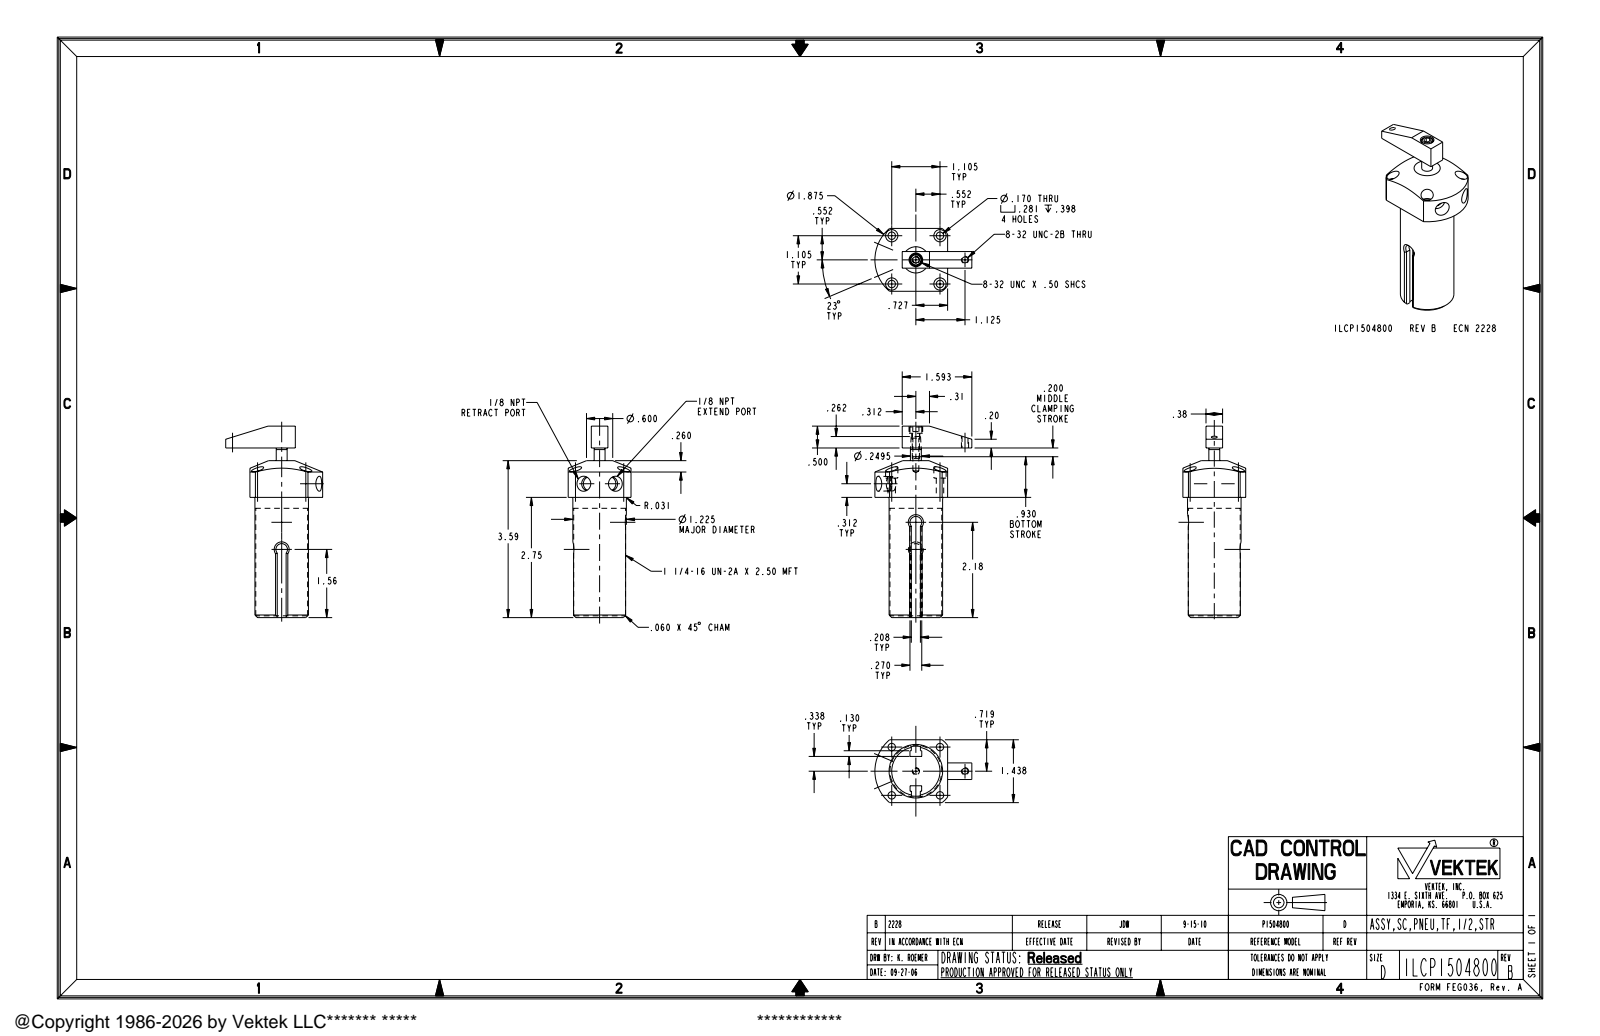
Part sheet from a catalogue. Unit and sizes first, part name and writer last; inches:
Units: inches
Overall size (bounding box): 4.38 × 2.219 × 1.438
Round holes (diameter × count): ⌀0.17 ×4, ⌀0.281 ×4, ⌀0.136 ×2, ⌀0.328 ×2, ⌀0.18 ×1, ⌀0.312 ×1
Round bosses / shafts (diameter × count): ⌀0.164 ×2, ⌀1.225 ×1, ⌀1.187 ×1, ⌀0.27 ×1, ⌀0.25 ×1
Partial cylindrical surfaces — rounded edges, fillets, slot ends (radius × count): R0.132 ×1, R0.135 ×1, R0.937 ×1
Main face-to-face distances: 0.529, 0.909, 2.75, 1.438, 0.031, 0.237, 0.38, 1.057, 0.528, 0.148
Hole centre spacings: 0.781, 1.105, 0.796, 1.562, 1.766, 1.125
Volume: 4.675 in³ · Surface area: 36.84 in²
Bodies: 2 solids, 123 faces (52 planar, 47 cylindrical, 24 other)
Part name (STEP PRODUCT): ILCP1504800; ILC91500503; ILCP1504800_ASM
STEP written by: PRO/ENGINEER BY PARAMETRIC TECHNOLOGY CORPORATION, 2007460 (AUTOMOTIVE_DESIGN_CC2)
